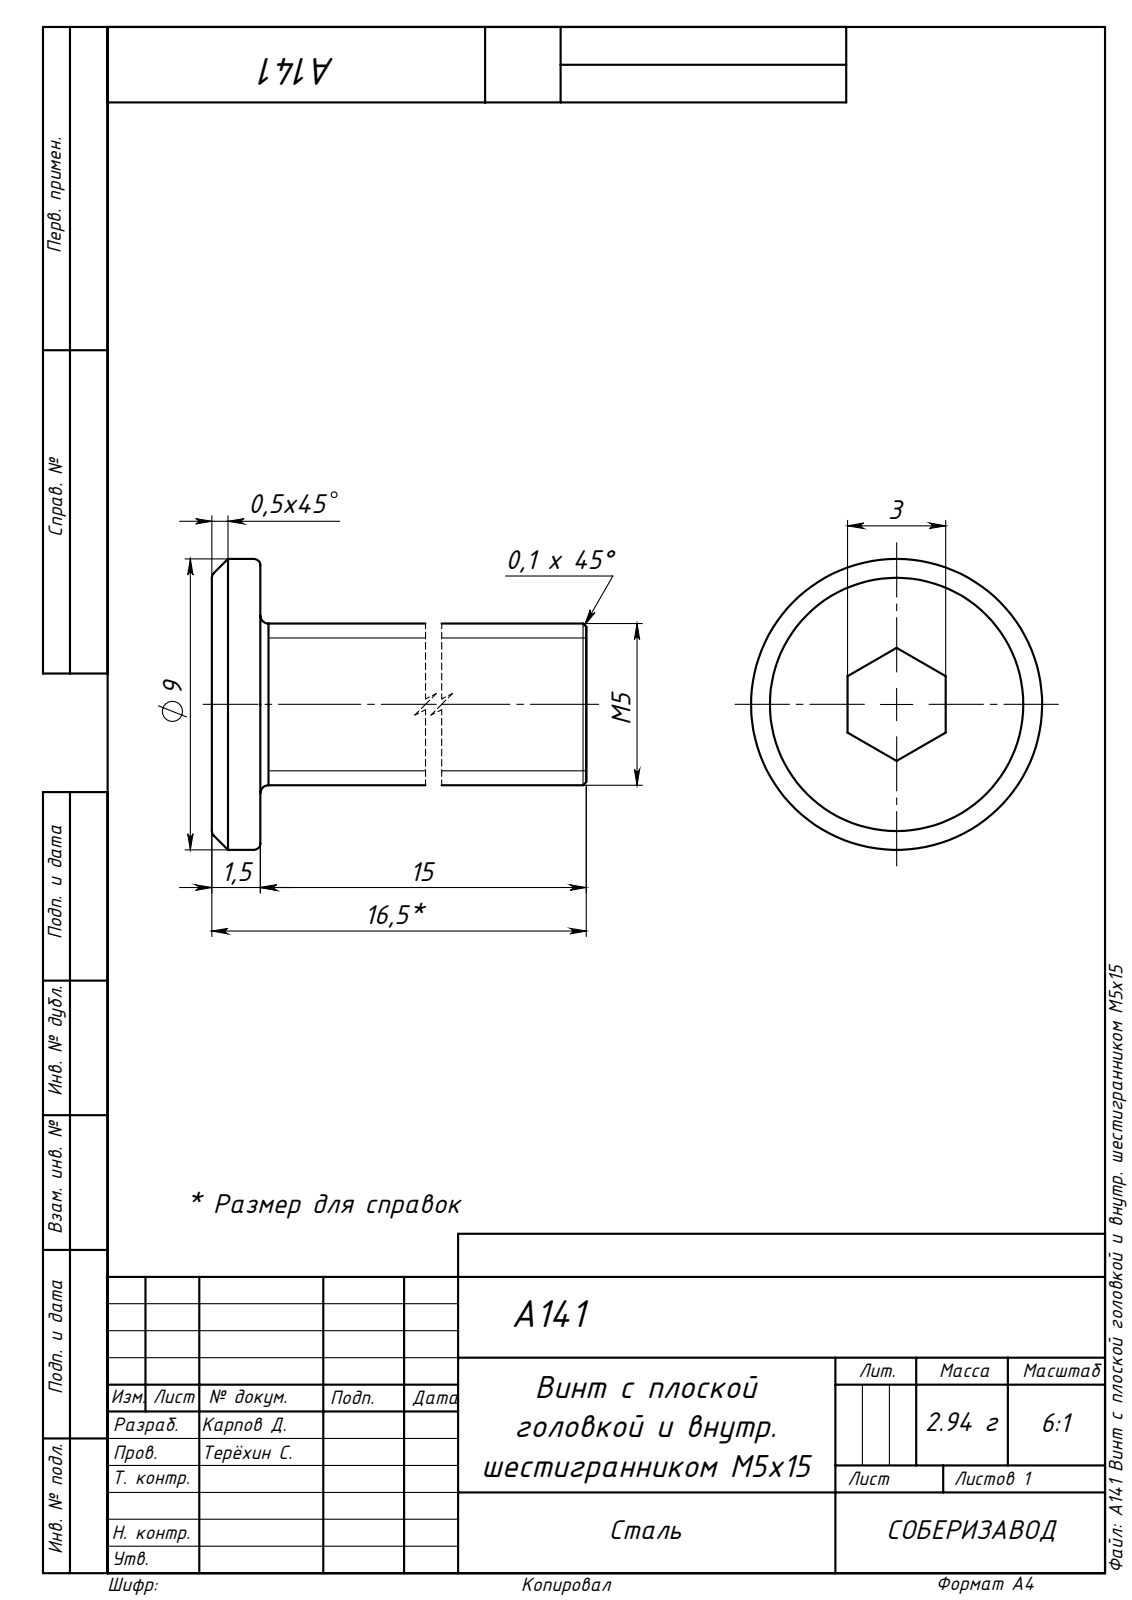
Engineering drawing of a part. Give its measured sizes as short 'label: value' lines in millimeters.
written by: SolidWorks 2020 (AUTOMOTIVE_DESIGN)
unit: mm
bodies: 1 solid, 24 faces (10 planar, 4 cylindrical, 10 other)
size: 16.5 × 9 × 9
volume: 374 mm³; area: 407 mm²
bosses: 1× ⌀9, 1× ⌀5
face distances: 1.5, 15, 16.5, 3.04
